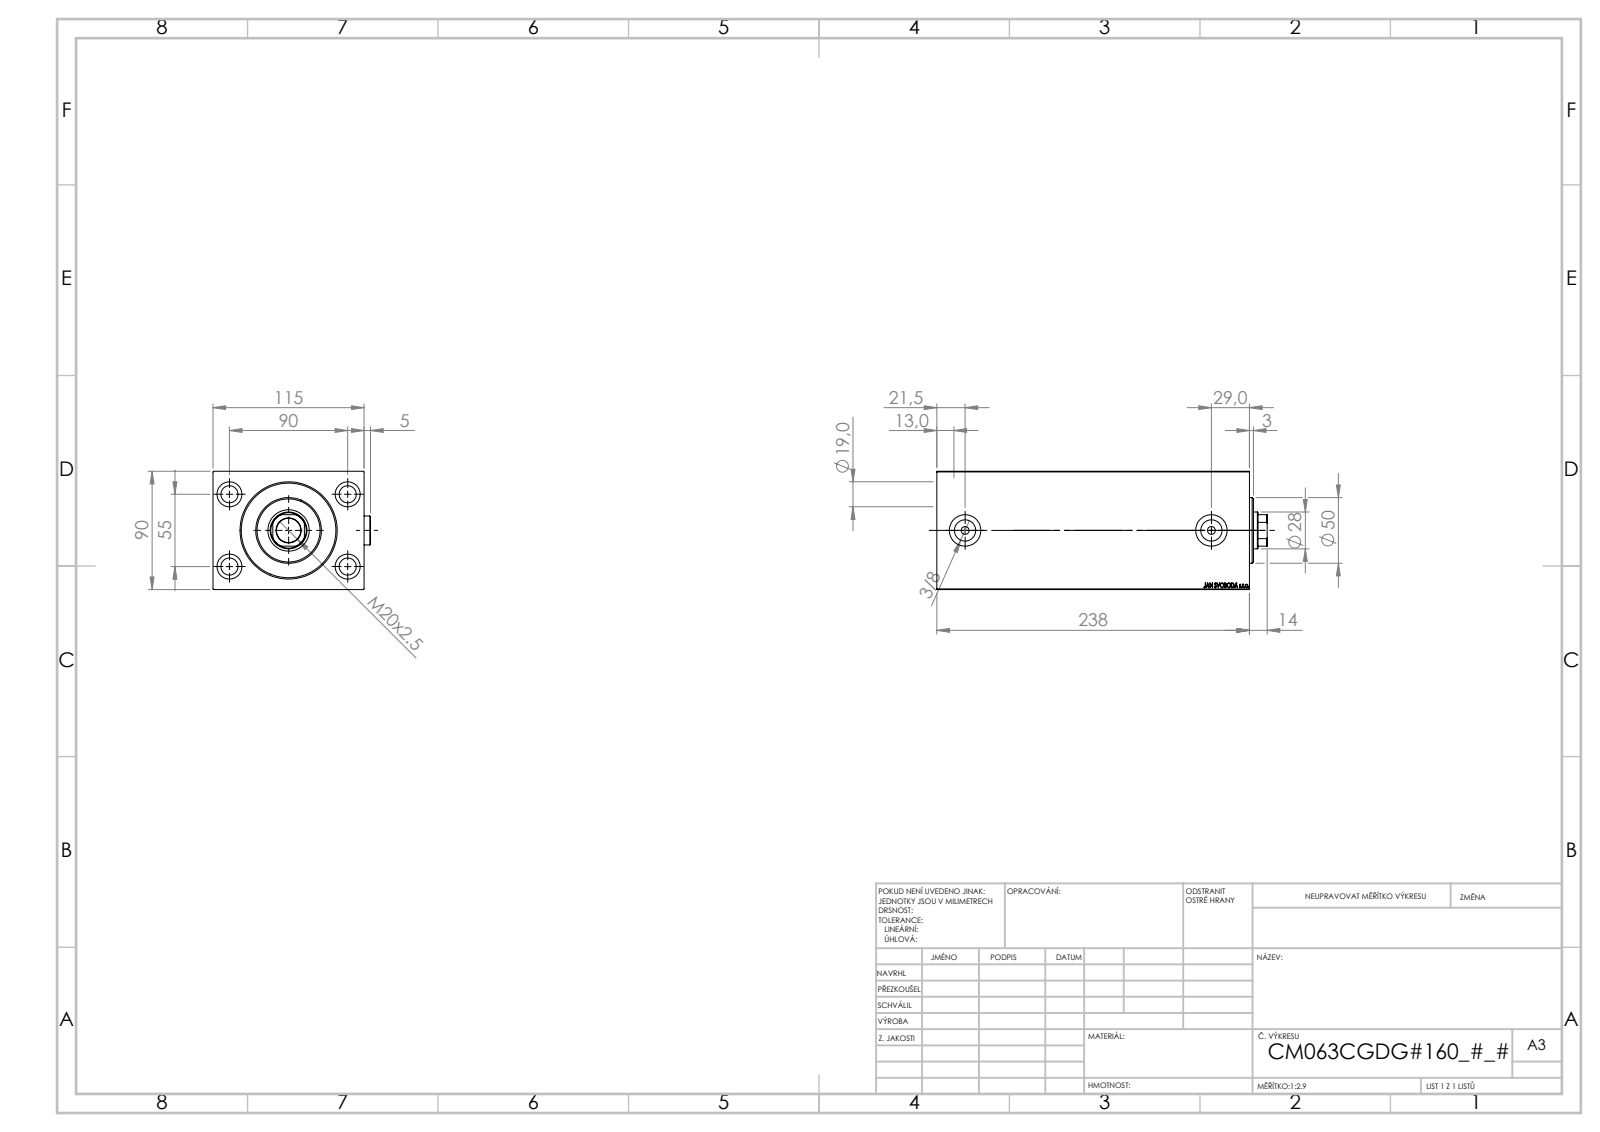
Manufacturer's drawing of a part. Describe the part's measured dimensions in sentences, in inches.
The part is named "V450CM_VC_B; V450CM_C_Body; V450CM_C_VCP; Zatka_OIL_PORT". Its 3-D file was written by "SolidWorks 2019 (CONFIG_CONTROL_DESIGN)". It is 4 solids with 919 faces: 443 planar, 78 cylindrical and 398 other. Overall it measures 9.902 by 4.72 by 3.543 inches. Its volume is 18.38 cubic inches and its surface area 391.2 square inches. Round holes: 4 of diameter 0.512, 4 of diameter 0.748, 2 of diameter 0.236, 2 of diameter 0.637, 2 of diameter 0.945, 1 of diameter 0.728, 1 of diameter 1.102, 1 of diameter 1.24, 1 of diameter 2.48, 1 of diameter 2.559, 1 of diameter 2.835. Round bosses or shafts: 2 of diameter 0.866, 1 of diameter 1.969. Partial cylindrical surfaces (rounded edges, fillets, slot ends): 1 of radius 0.531. The main face-to-face distances are 3.543, 4.528, 9.37, 0.689, 8.681, 0.531, 8.15, 8.839, 2.539, 6.831. The hole center spacings are 2.076, 2.165, 3.543, 4.153, 7.382.
